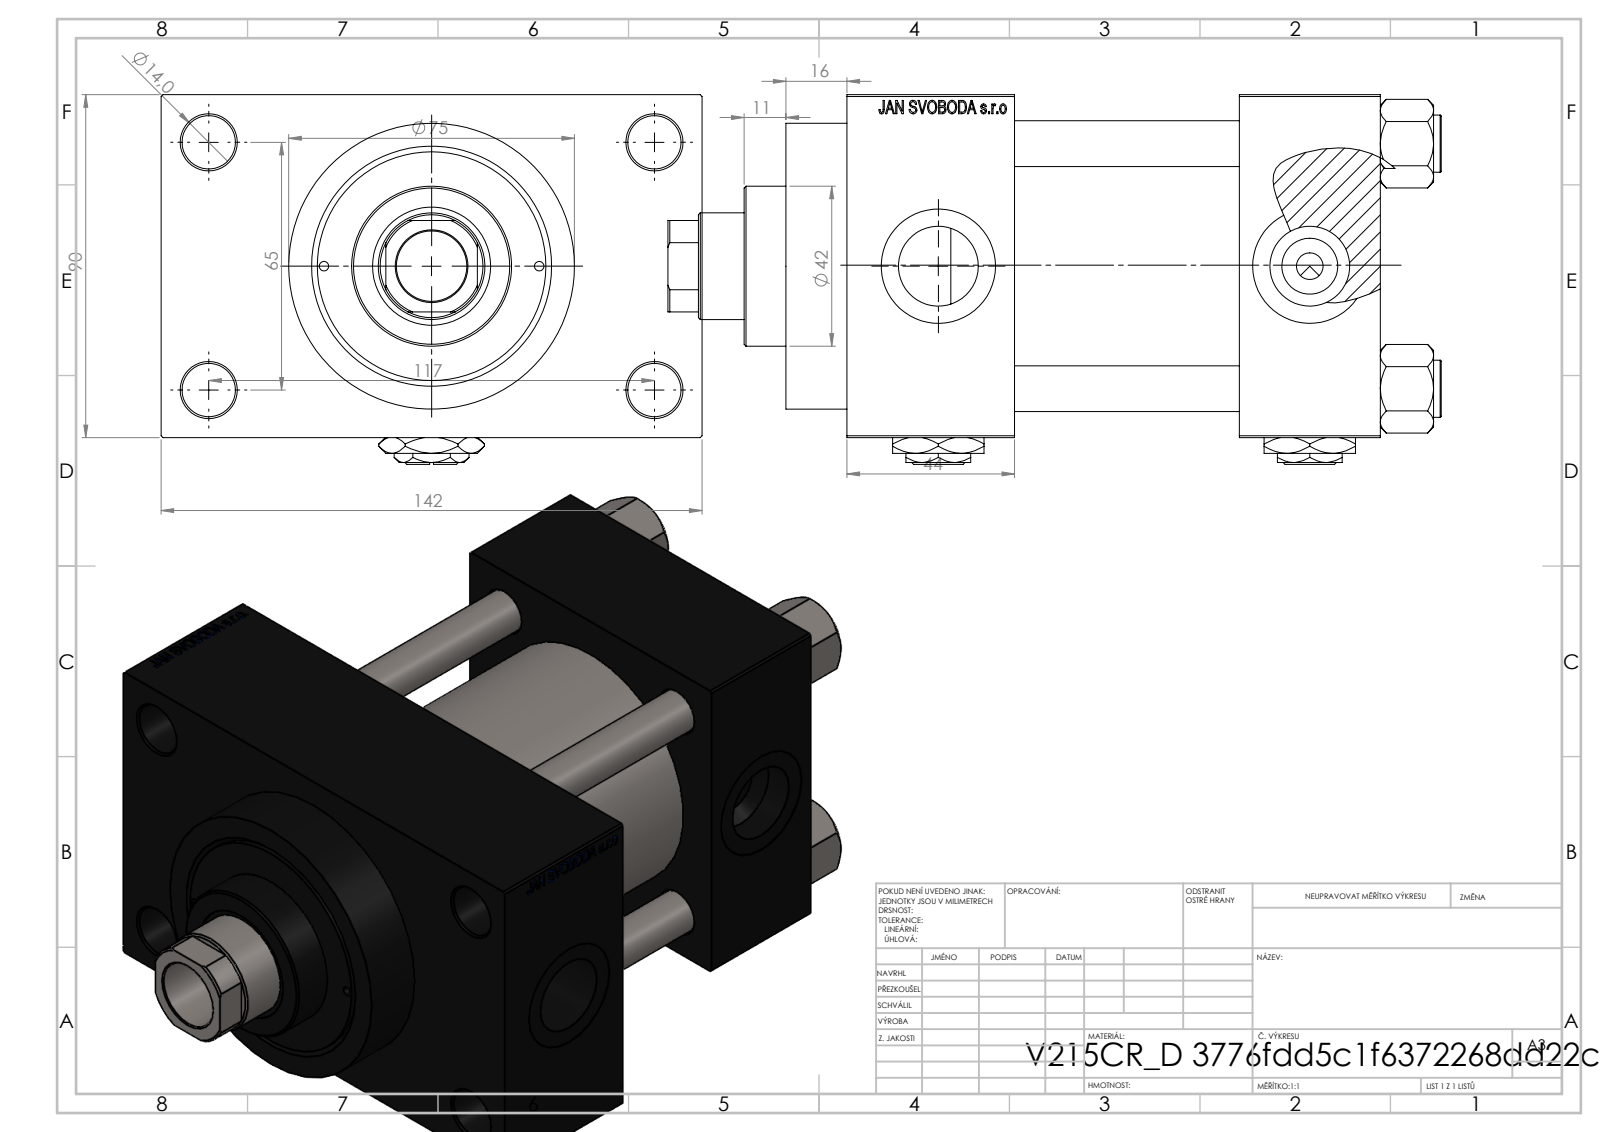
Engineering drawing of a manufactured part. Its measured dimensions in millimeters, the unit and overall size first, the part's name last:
Units: millimetres
Overall size (bounding box): 203 × 142 × 97
Round holes (diameter × count): ⌀12 ×4, ⌀14 ×4, ⌀20.96 ×4, ⌀30 ×4, ⌀7 ×3, ⌀2.5 ×2, ⌀18.5 ×1, ⌀28 ×1, ⌀31 ×1, ⌀50 ×1, ⌀60 ×1, ⌀63 ×1
Round bosses / shafts (diameter × count): ⌀15 ×4, ⌀75 ×1, ⌀69 ×1, ⌀42 ×1
Partial cylindrical surfaces — rounded edges, fillets, slot ends (radius × count): R13.5 ×1
Main face-to-face distances: 90, 59, 37, 96, 140, 103, 44, 26, 116, 142
Hole centre spacings: 26.35, 32.39, 44.4, 45.47, 64.3, 66.92, 68.42, 69.81
Volume: 1 091 000 mm³ · Surface area: 204 743 mm²
Bodies: 13 solids, 1212 faces (547 planar, 103 cylindrical, 562 other)
Part name (STEP PRODUCT): V215CR_D_Body; V215_VC_A; Zatka_pro_OIL_PORT; V215CR_D_TYCINKA (+2 more)
STEP written by: SolidWorks 2019 (CONFIG_CONTROL_DESIGN)
